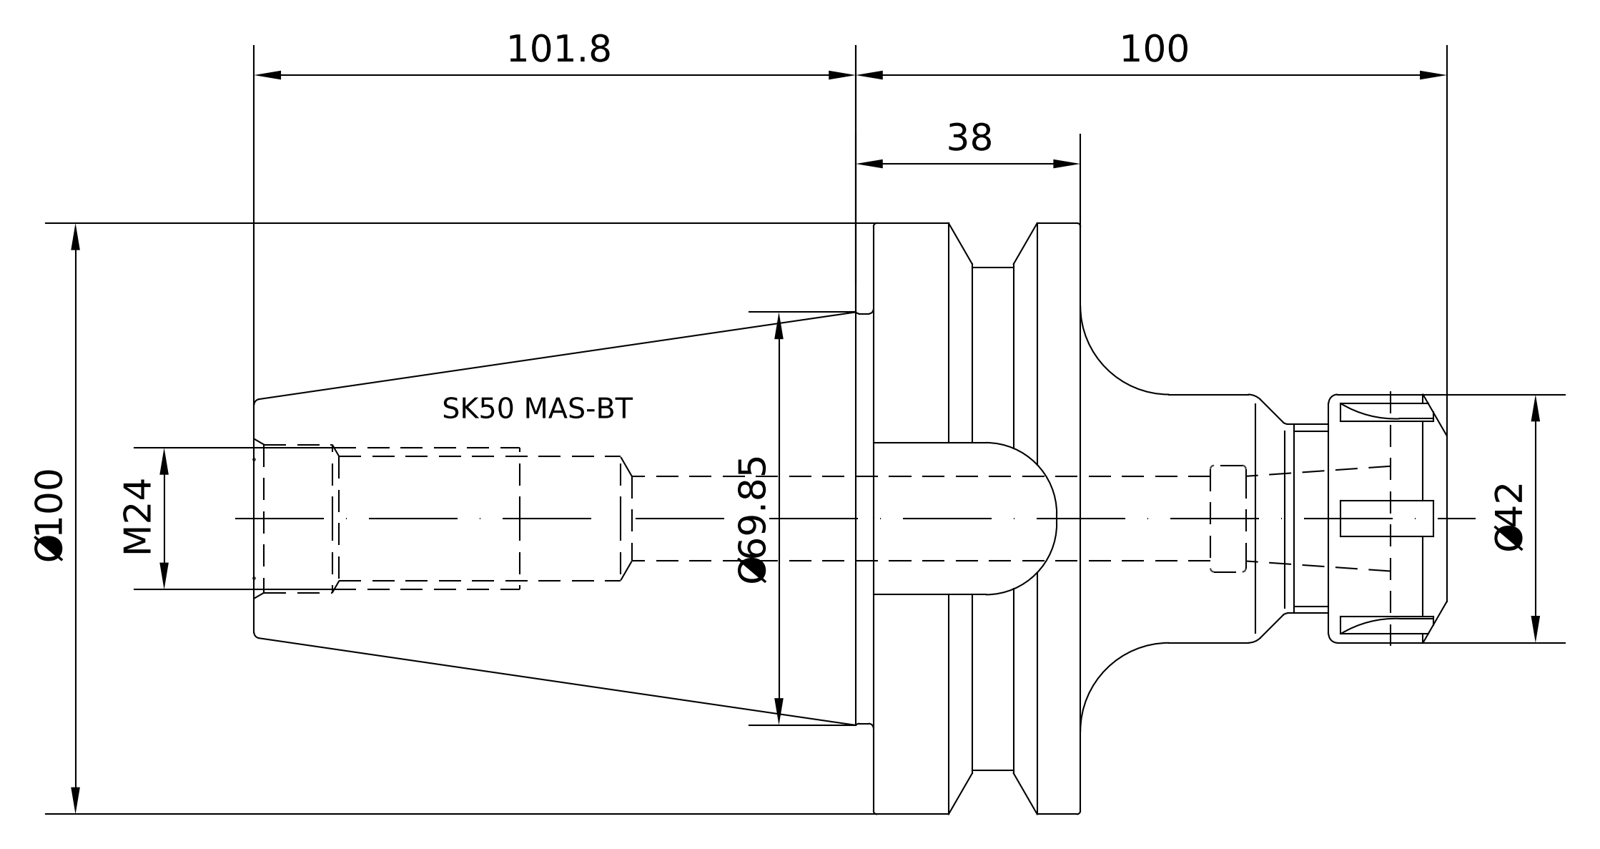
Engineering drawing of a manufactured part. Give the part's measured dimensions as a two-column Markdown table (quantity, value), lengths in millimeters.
| quantity | value |
| --- | --- |
| part name | 50-521-25; 83-912-25; 50-521-25_ASM |
| STEP written by | PRO/ENGINEER BY PARAMETRIC TECHNOLOGY CORPORATION, 2010430 (CONFIG_CONTROL_DESIGN) |
| units | millimeters |
| bodies | 2 solids, 146 faces (46 planar, 26 cylindrical, 74 other) |
| overall size | 201.8 × 99.97 × 99.97 |
| volume | 545 728 mm³ |
| surface area | 64 533 mm² |
| round holes (diameter × count) | 18 × 1, 20.75 × 1, 25.02 × 1, 25.7 × 1 |
| round bosses / shafts (diameter × count) | 99.97 × 1, 84.75 × 1, 69.15 × 1, 42 × 1, 32 × 1, 24.01 × 1 |
| partial cylindrical surfaces (radius × count) | 12.9 × 1 |
| main face-to-face distances | 35, 77, 42, 70.4, 97, 62, 20, 104.8, 139.8, 181.8 |
